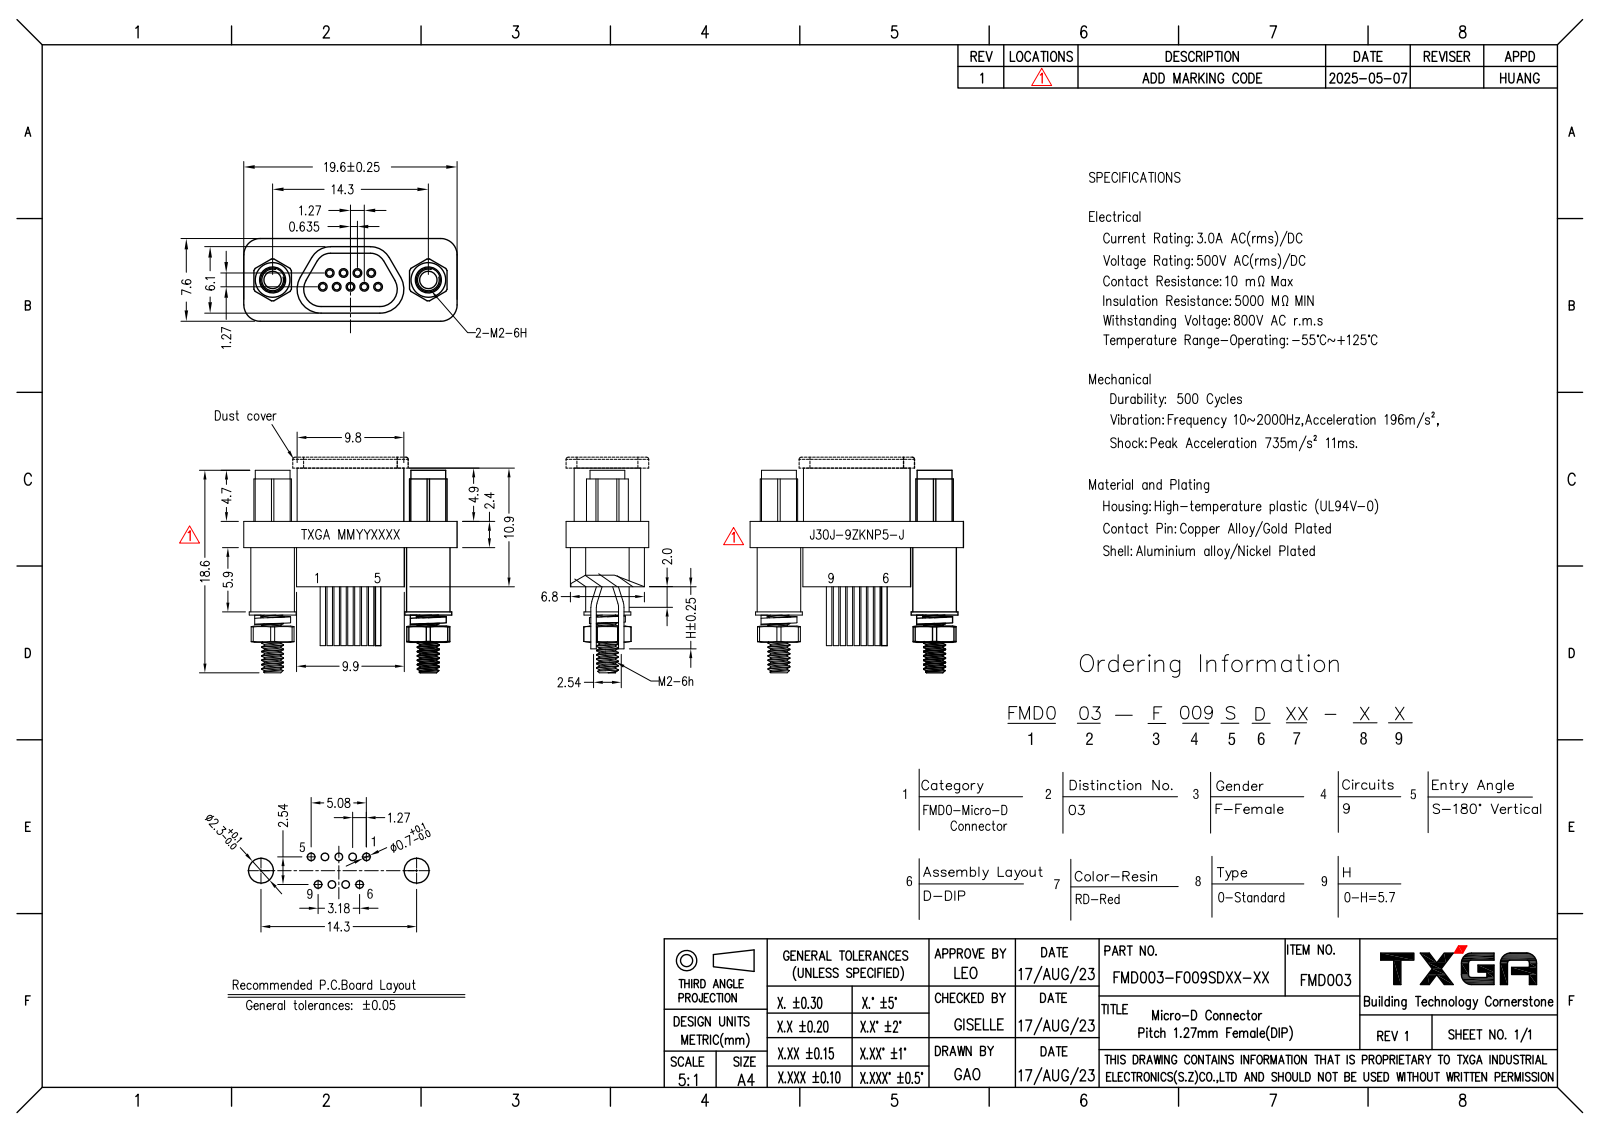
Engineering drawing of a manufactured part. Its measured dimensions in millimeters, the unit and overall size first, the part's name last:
Units: millimetres
Overall size (bounding box): 19.6 × 18.8 × 7.6
Round holes (diameter × count): ⌀0.6 ×9, ⌀0.8 ×9, ⌀1.6 ×2, ⌀2.3 ×2, ⌀3.2 ×2
Round bosses / shafts (diameter × count): ⌀0.5 ×27, ⌀4.3 ×2, ⌀4 ×2, ⌀3.15 ×2, ⌀2 ×2
Partial cylindrical surfaces — rounded edges, fillets, slot ends (radius × count): R0.1 ×15, R0.2 ×12, R1.5 ×4, R1.8 ×4, R1.4 ×2, R1.6 ×2, R2 ×2, R2.2 ×2
Main face-to-face distances: 6, 2.4, 3.5, 3.6, 0.6, 0.4, 1.3, 7.2, 0.7, 6.85
Hole centre spacings: 1.43, 1.27, 2.3, 3.43, 2.54, 2.29, 2.55, 3.81
Volume: 943 mm³ · Surface area: 2 163 mm²
Bodies: 20 solids, 858 faces (297 planar, 329 cylindrical, 232 other)
Part name (STEP PRODUCT): ZHUTI-9_5; MANIFOLD_SOLID_BREP_19780; MANIFOLD_SOLID_BREP_30884; LUOSI-9_5_ASM (+8 more)
STEP written by: PRO/ENGINEER BY PARAMETRIC TECHNOLOGY CORPORATION, 2010280 (CONFIG_CONTROL_DESIGN)
